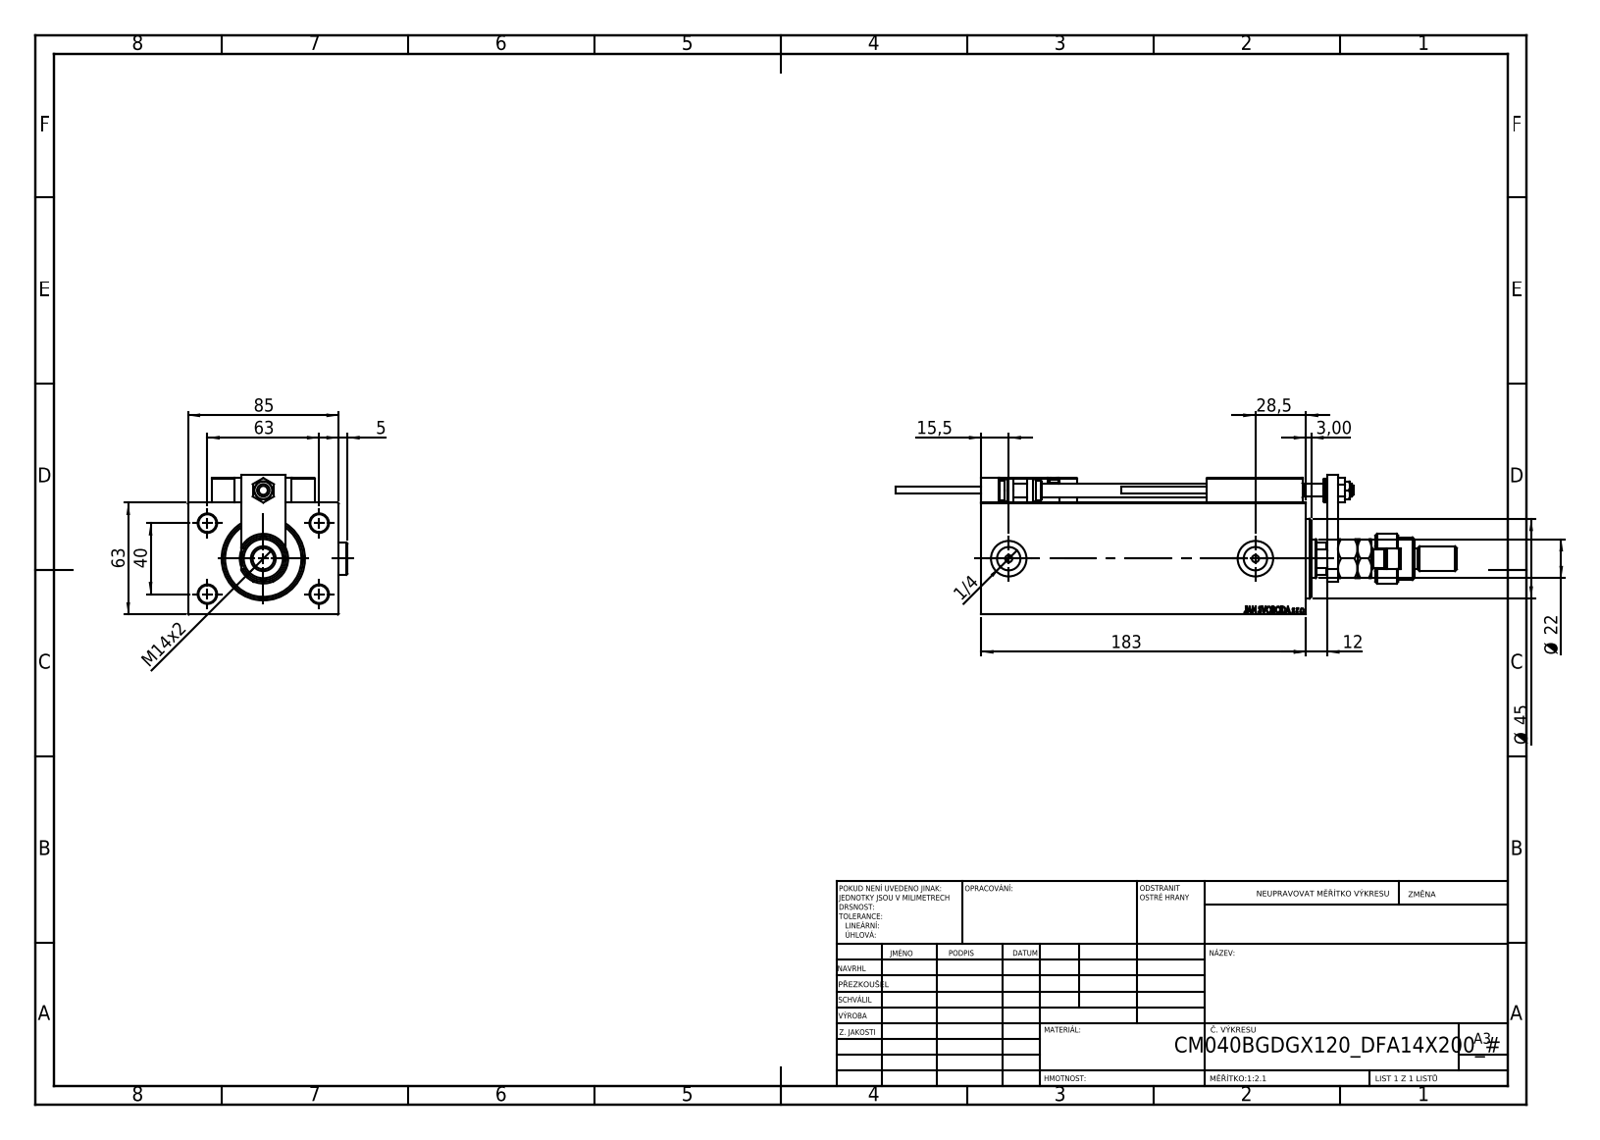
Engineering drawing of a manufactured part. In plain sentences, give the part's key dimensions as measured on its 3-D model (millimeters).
The part is named "ZARAZKA; NUT_D12; TYC_L79; V450CM_B_Body (+8 more)". Its 3-D file was written by "SolidWorks 2019 (CONFIG_CONTROL_DESIGN)". It is 28 solids with 1457 faces: 623 planar, 213 cylindrical and 621 other. Overall it measures 316 by 89.9 by 78.5 millimeters. Its volume is 936 514 cubic millimeters and its surface area 154 413 square millimeters. Round holes: 6 of diameter 4, 5 of diameter 8, 4 of diameter 3.2, 4 of diameter 10, 2 of diameter 5, 2 of diameter 13.16, 2 of diameter 20, 1 of diameter 7, 1 of diameter 12.5, 1 of diameter 16.5, 1 of diameter 22, 1 of diameter 25.5. Round bosses or shafts: 3 of diameter 18, 2 of diameter 11, 2 of diameter 5, 2 of diameter 3.8, 1 of diameter 28, 1 of diameter 24, 1 of diameter 14, 1 of diameter 13. Partial cylindrical surfaces (rounded edges, fillets, slot ends): 30 of radius 0.3, 2 of radius 3, 1 of radius 9.75, 1 of radius 10.5. The main face-to-face distances are 63, 85, 12, 171, 183, 14, 30, 18, 77, 15. The hole center spacings are 37.31, 11.37, 20, 29.59, 29.69, 36.06, 36.53, 40.
